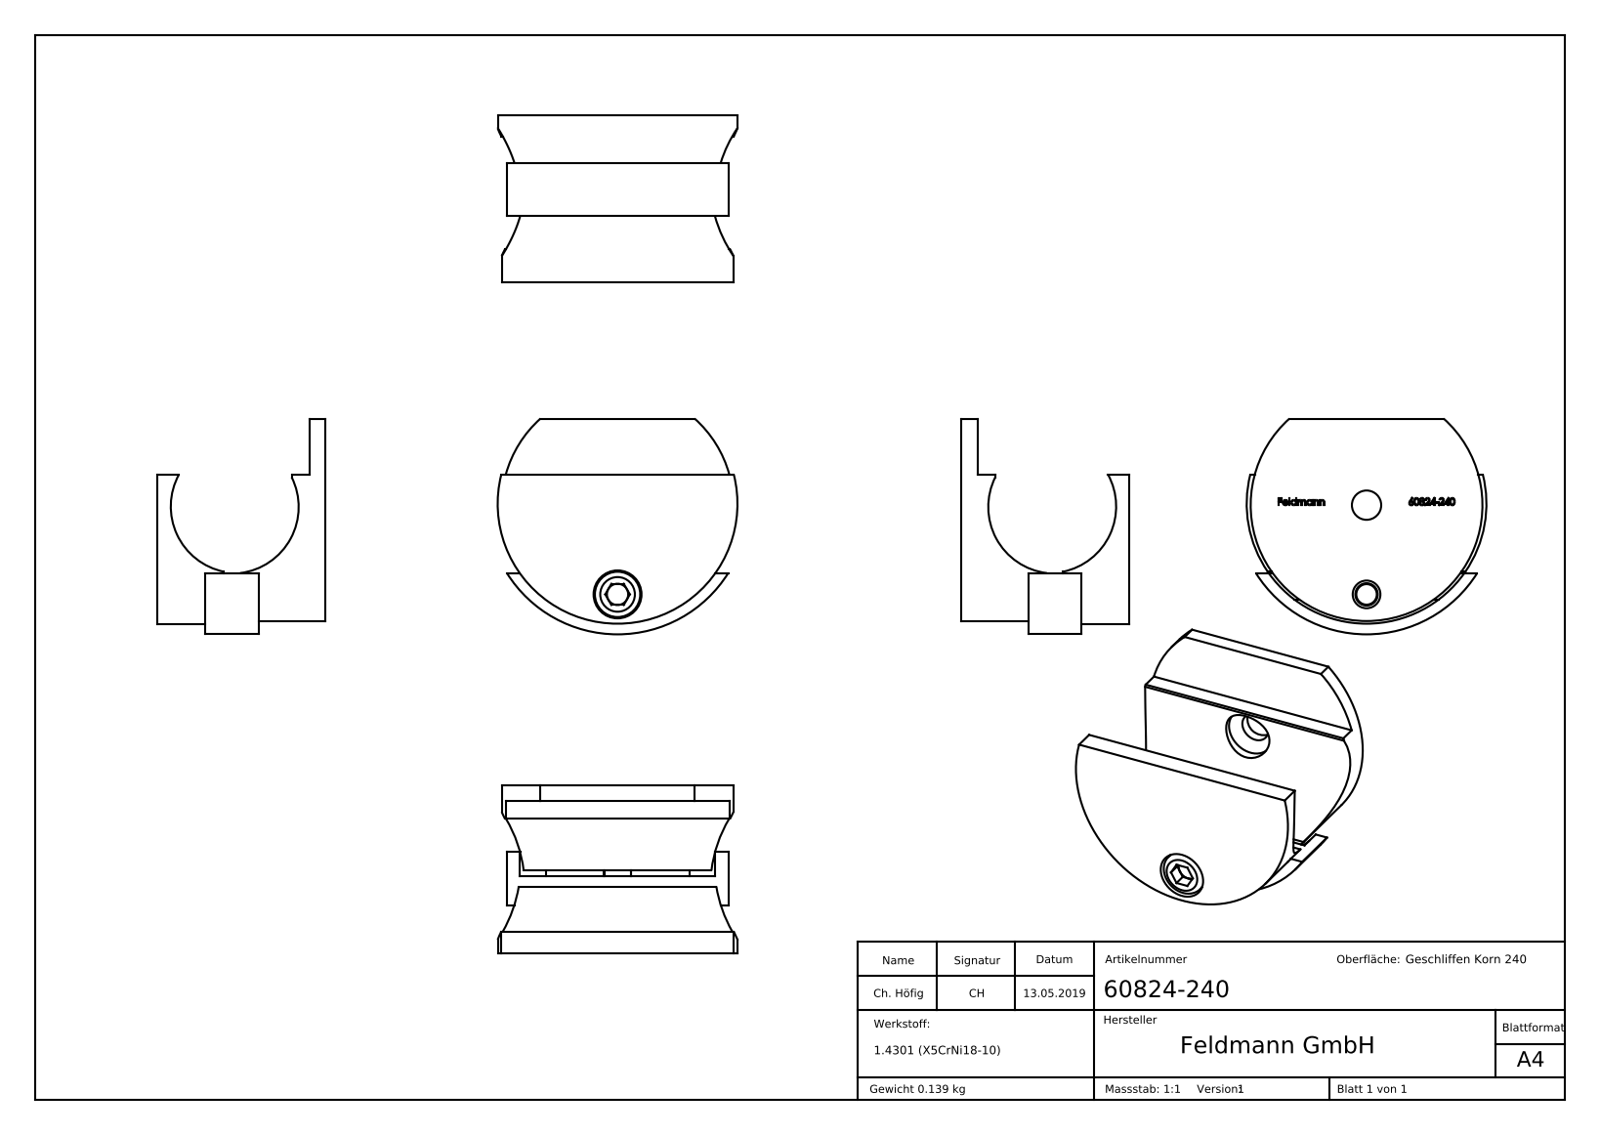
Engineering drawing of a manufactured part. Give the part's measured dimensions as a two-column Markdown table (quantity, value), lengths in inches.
| quantity | value |
| --- | --- |
| part name | 60824-240 Teil3_60824-240 Teil3; DIN 912 M5x20_DIN 912 M5x20; 60824-240 Teil1_60824-240 Teil1; 60824-240 Teil2_60824-240 Teil2 (+1 more) |
| STEP written by | SolidWorks 2015 (CONFIG_CONTROL_DESIGN) |
| units | inches |
| bodies | 4 solids, 303 faces (159 planar, 28 cylindrical, 116 other) |
| overall size | 1.772 × 1.594 × 1.24 |
| volume | 1.072 in³ |
| surface area | 15.57 in² |
| round holes (diameter × count) | 0.217 × 2, 0.165 × 1, 0.354 × 1, 0.362 × 1 |
| round bosses / shafts (diameter × count) | 0.335 × 1, 0.197 × 1 |
| partial cylindrical surfaces (radius × count) | 0.492 × 2, 0.856 × 1, 0.886 × 1, 0.965 × 1 |
| main face-to-face distances | 1.24, 0.63, 0.118, 0.492, 0.748, 1.122, 0.512, 0.61, 0.551, 0.256 |
| hole center spacings | 0.659 |
